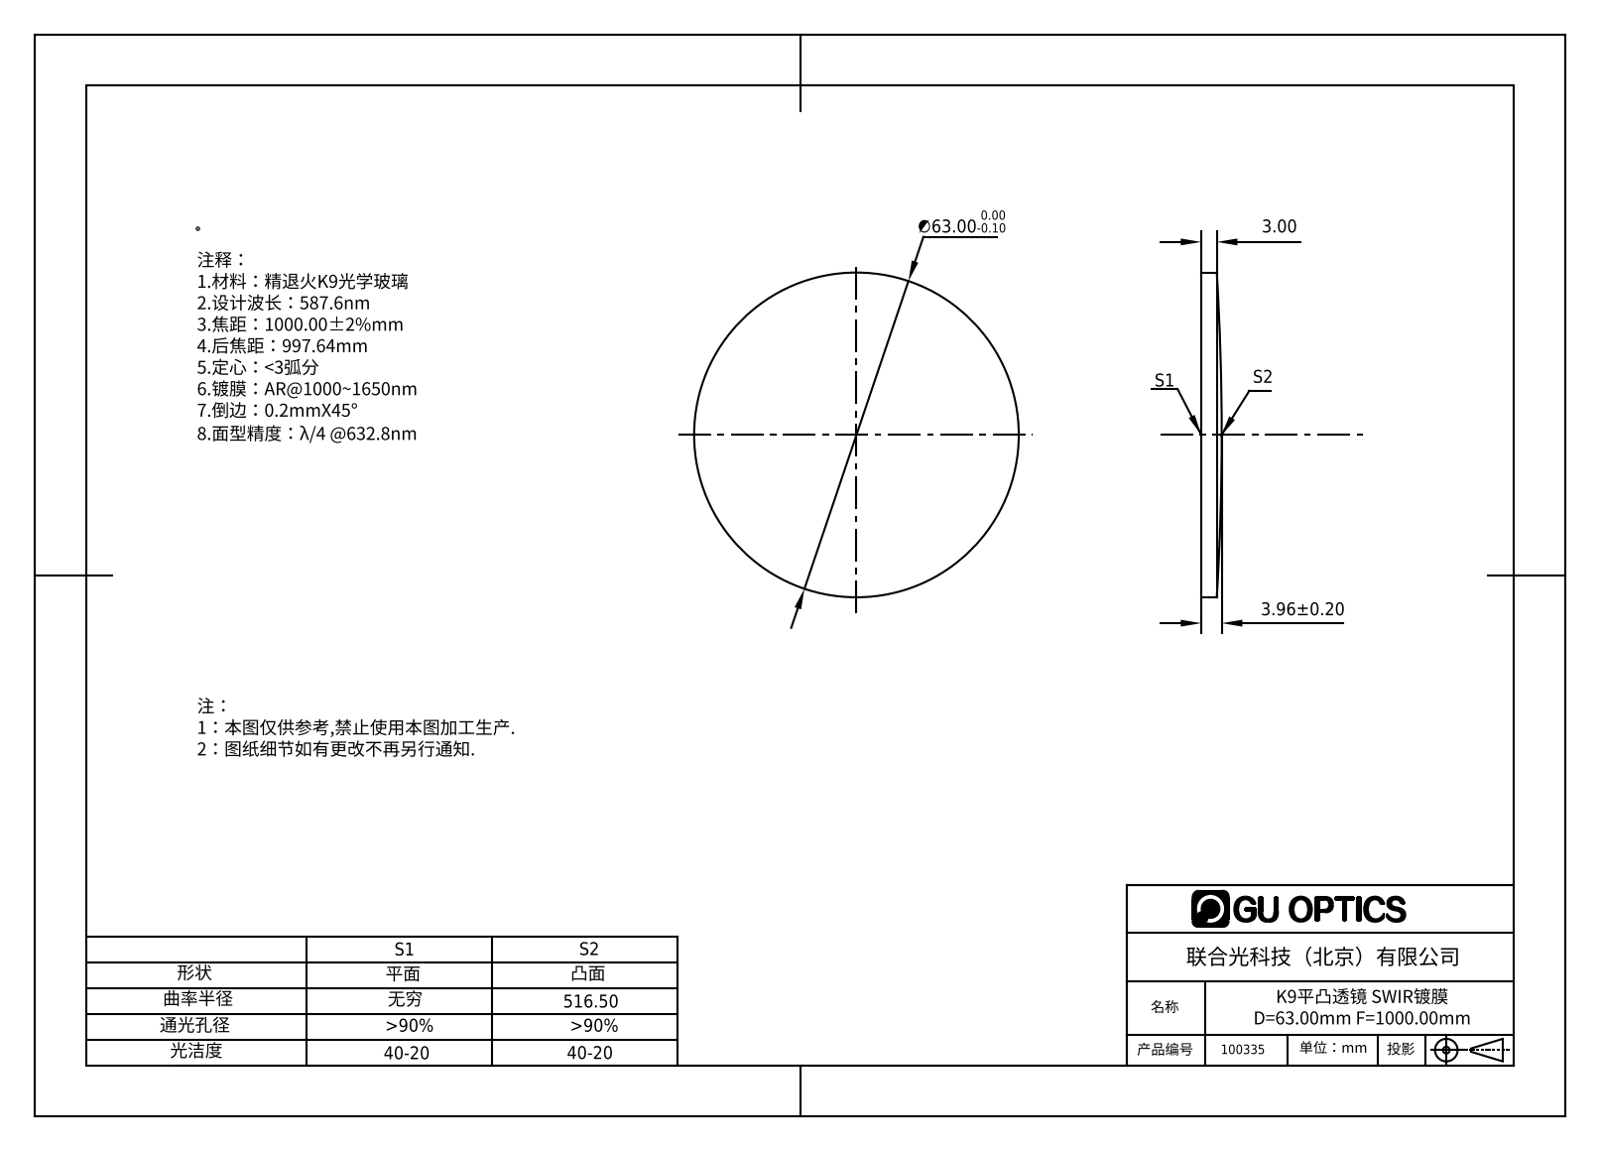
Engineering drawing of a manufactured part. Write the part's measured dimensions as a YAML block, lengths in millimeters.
part_name: "100163"
step_written_by: "SolidWorks 2016 (AUTOMOTIVE_DESIGN)"
units: millimeters
bodies: {solids: 1, faces: 5, planar: 1, cylindrical: 2, other: 2}
overall_size: [63, 63, 3.96]
volume: 10848
surface_area: 6831
round_bosses_or_shafts:
  - {diameter: 63, count: 1}
